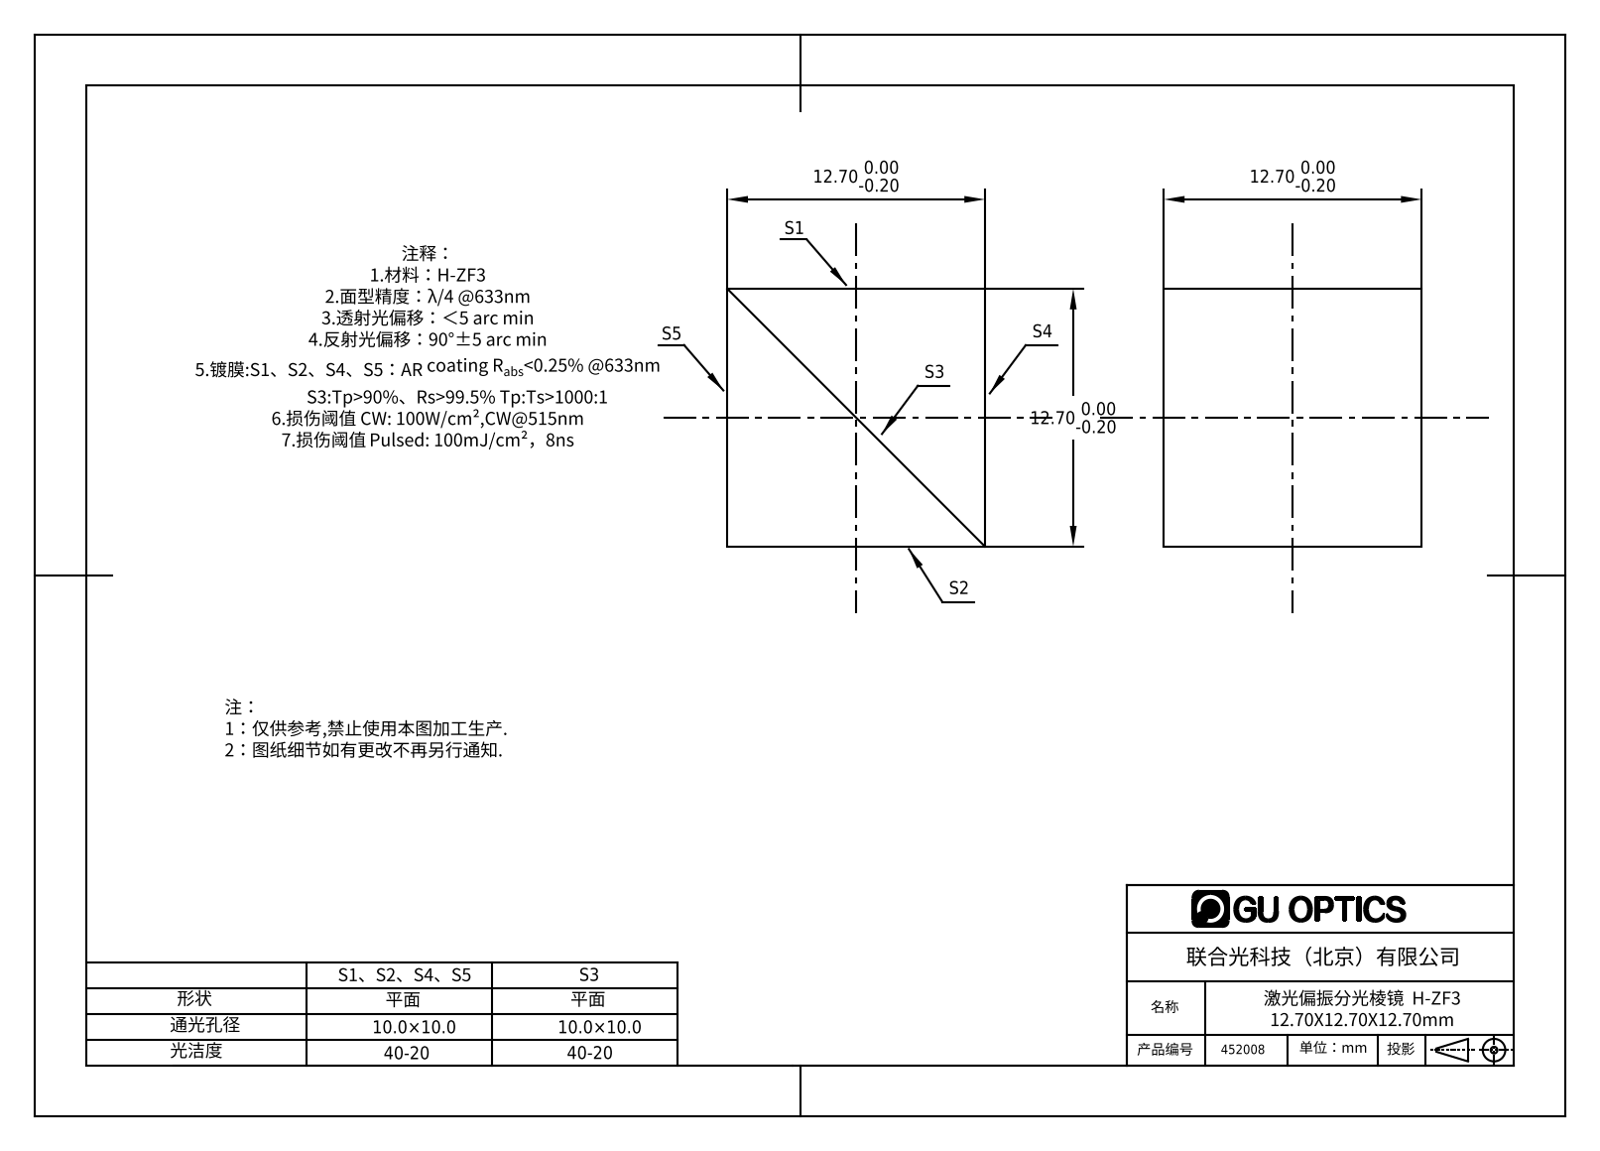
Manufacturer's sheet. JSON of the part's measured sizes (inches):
{"part_name": "452005", "step_written_by": "SolidWorks 2016 (AUTOMOTIVE_DESIGN)", "units": "inches", "bodies": {"solids": 2, "faces": 10, "planar": 10, "cylindrical": 0, "other": 0}, "overall_size": [0.5, 0.5, 0.5], "volume_in3": 0.125, "surface_area_in2": 2.207, "face_to_face_distances": [0.5]}
